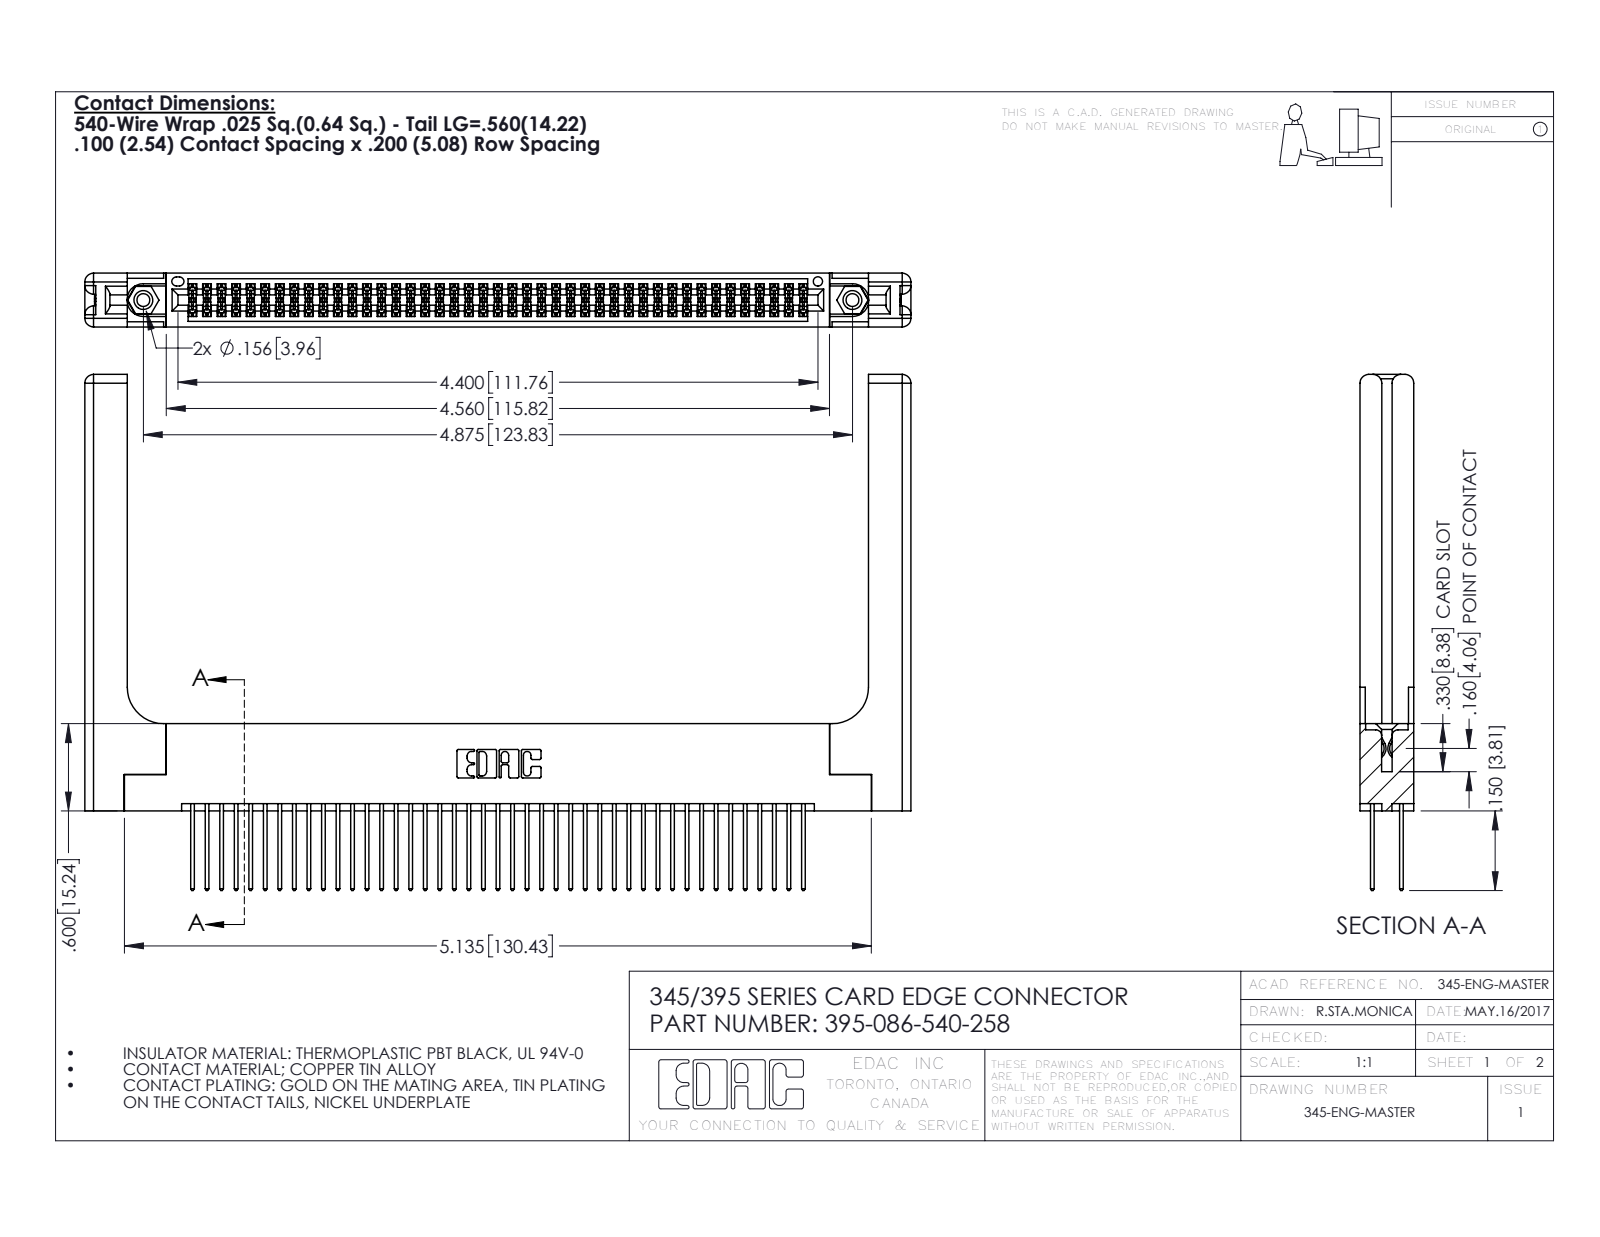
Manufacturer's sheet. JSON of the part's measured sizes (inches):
{"part_name": "345-250-001_345-250-001-102; 345 Part_Flush Mounting Lugs - 0.156 Dia-TH; 345-292-001_345-293-140; 345-220-058_345-220-058 (+1 more)", "step_written_by": "SolidWorks 2016 (CONFIG_CONTROL_DESIGN)", "units": "inches", "bodies": {"solids": 91, "faces": 4682, "planar": 3066, "cylindrical": 1556, "other": 60}, "overall_size": [5.679, 3.547, 0.37], "volume_in3": 1.393, "surface_area_in2": 43.09, "round_holes": [[0.089, 2], [0.125, 2], [0.156, 2], [0.064, 1]], "round_bosses_or_shafts": [[0.155, 2]], "partial_cylinders_radius": [[0.006, 129], [0.01, 86], [0.01, 22], [0.06, 16], [0.007, 6], [0.031, 6], [0.026, 3], [0.014, 2]], "face_to_face_distances": [0.072, 0.298, 0.37, 0.2, 0.098, 0.272, 0.025, 0.225, 0.175, 0.148], "hole_center_spacings": [0.27, 4.639, 4.875]}
